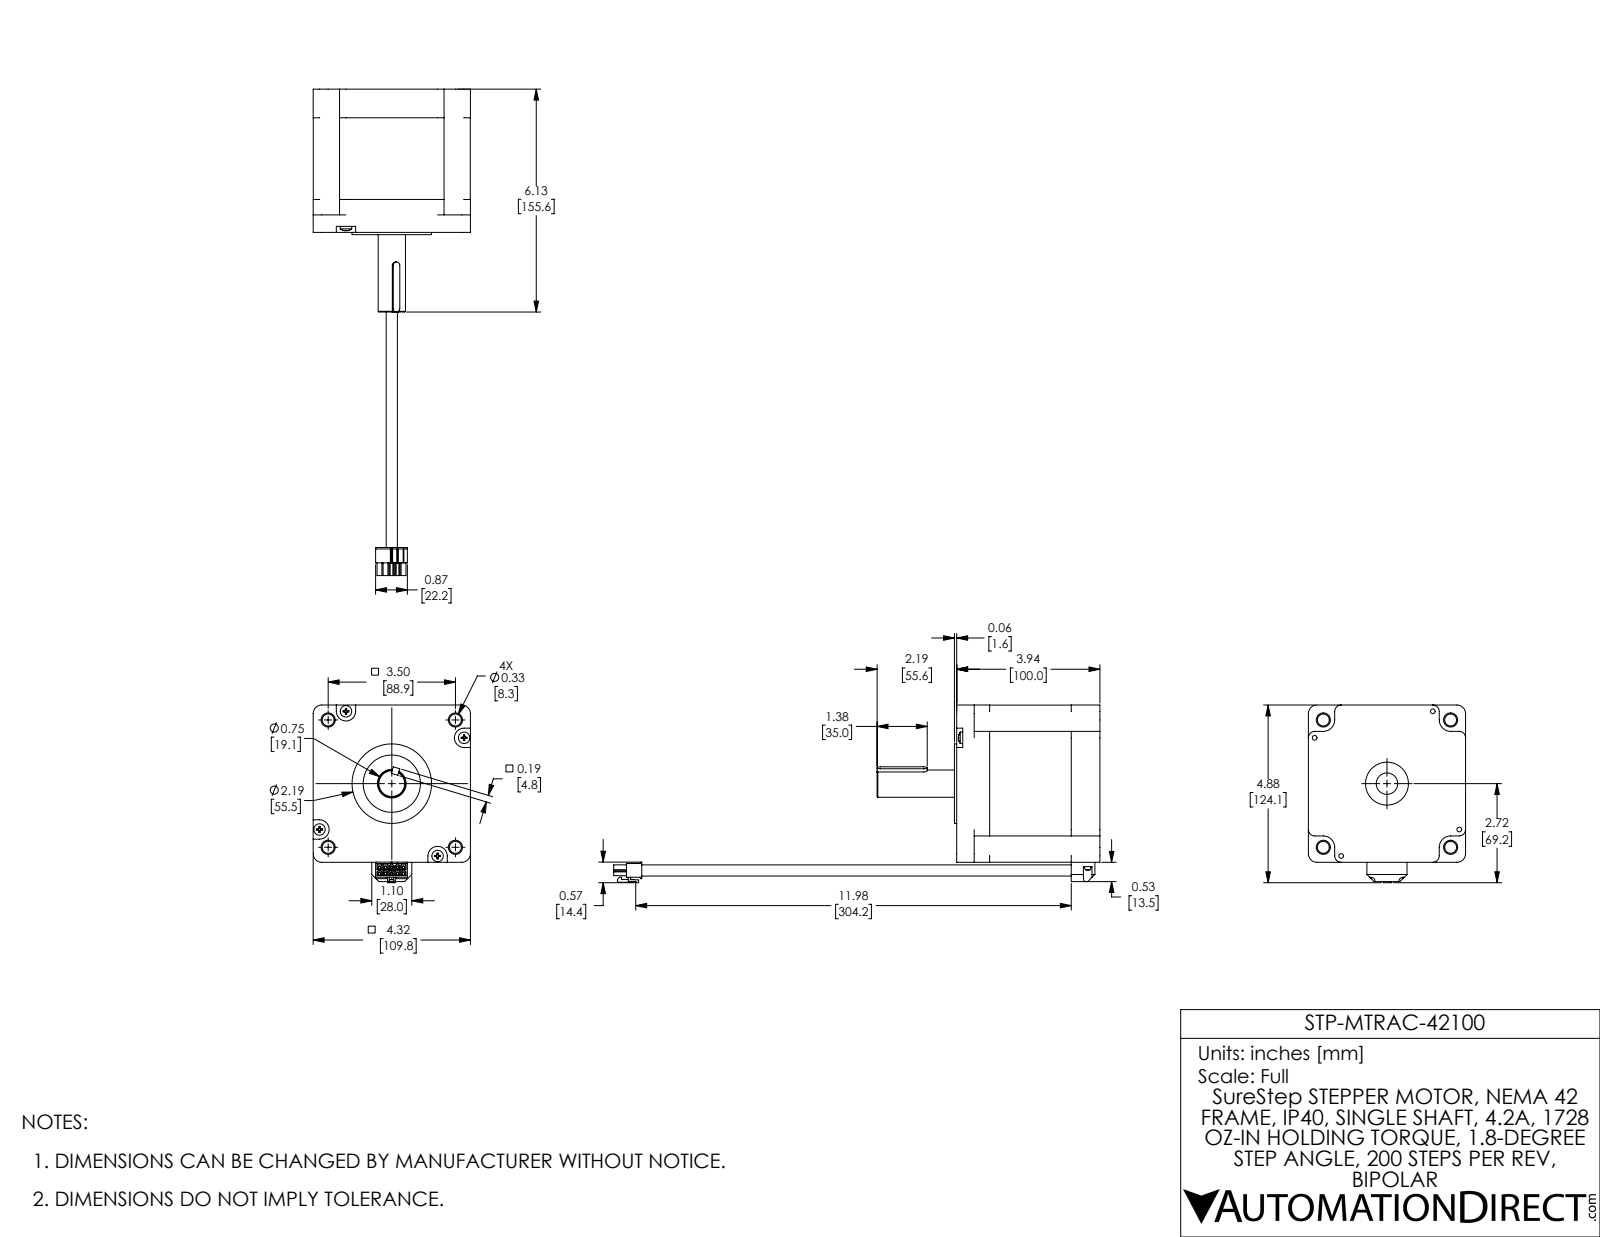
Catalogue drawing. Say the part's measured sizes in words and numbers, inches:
The part is named "STP-MTRAC-42100". Its 3-D file was written by "SolidWorks 2017 (AUTOMOTIVE_DESIGN)". It is 13 solids with 999 faces: 602 planar, 205 cylindrical and 192 other. Overall it measures 13.37 by 4.884 by 4.323 inches. Its volume is 37.11 cubic inches and its surface area 287 square inches. Round holes: 8 of diameter 0.177, 6 of diameter 0.13, 4 of diameter 0.181, 4 of diameter 0.327, 1 of diameter 0.591, 1 of diameter 0.787, 1 of diameter 1.116, 1 of diameter 1.181, 1 of diameter 1.378, 1 of diameter 1.575, 1 of diameter 1.627, 1 of diameter 2.047. Round bosses or shafts: 4 of diameter 0.315, 4 of diameter 0.157, 2 of diameter 0.177, 1 of diameter 2.579, 1 of diameter 2.559, 1 of diameter 2.186, 1 of diameter 1.207, 1 of diameter 1. Partial cylindrical surfaces (rounded edges, fillets, slot ends): 22 of radius 0.012, 16 of radius 0.177, 6 of radius 0.01, 4 of radius 0.236, 4 of radius 0.266, 4 of radius 0.315, 2 of radius 0.094, 2 of radius 0.118. The main face-to-face distances are 4.321, 0.669, 3.937, 2.854, 4.319, 0.787, 3.15, 3.031, 2.244, 0.906. The hole center spacings are 0.545, 2.354, 3.019, 3.329, 3.77, 4.799, 1.03, 2.475.
